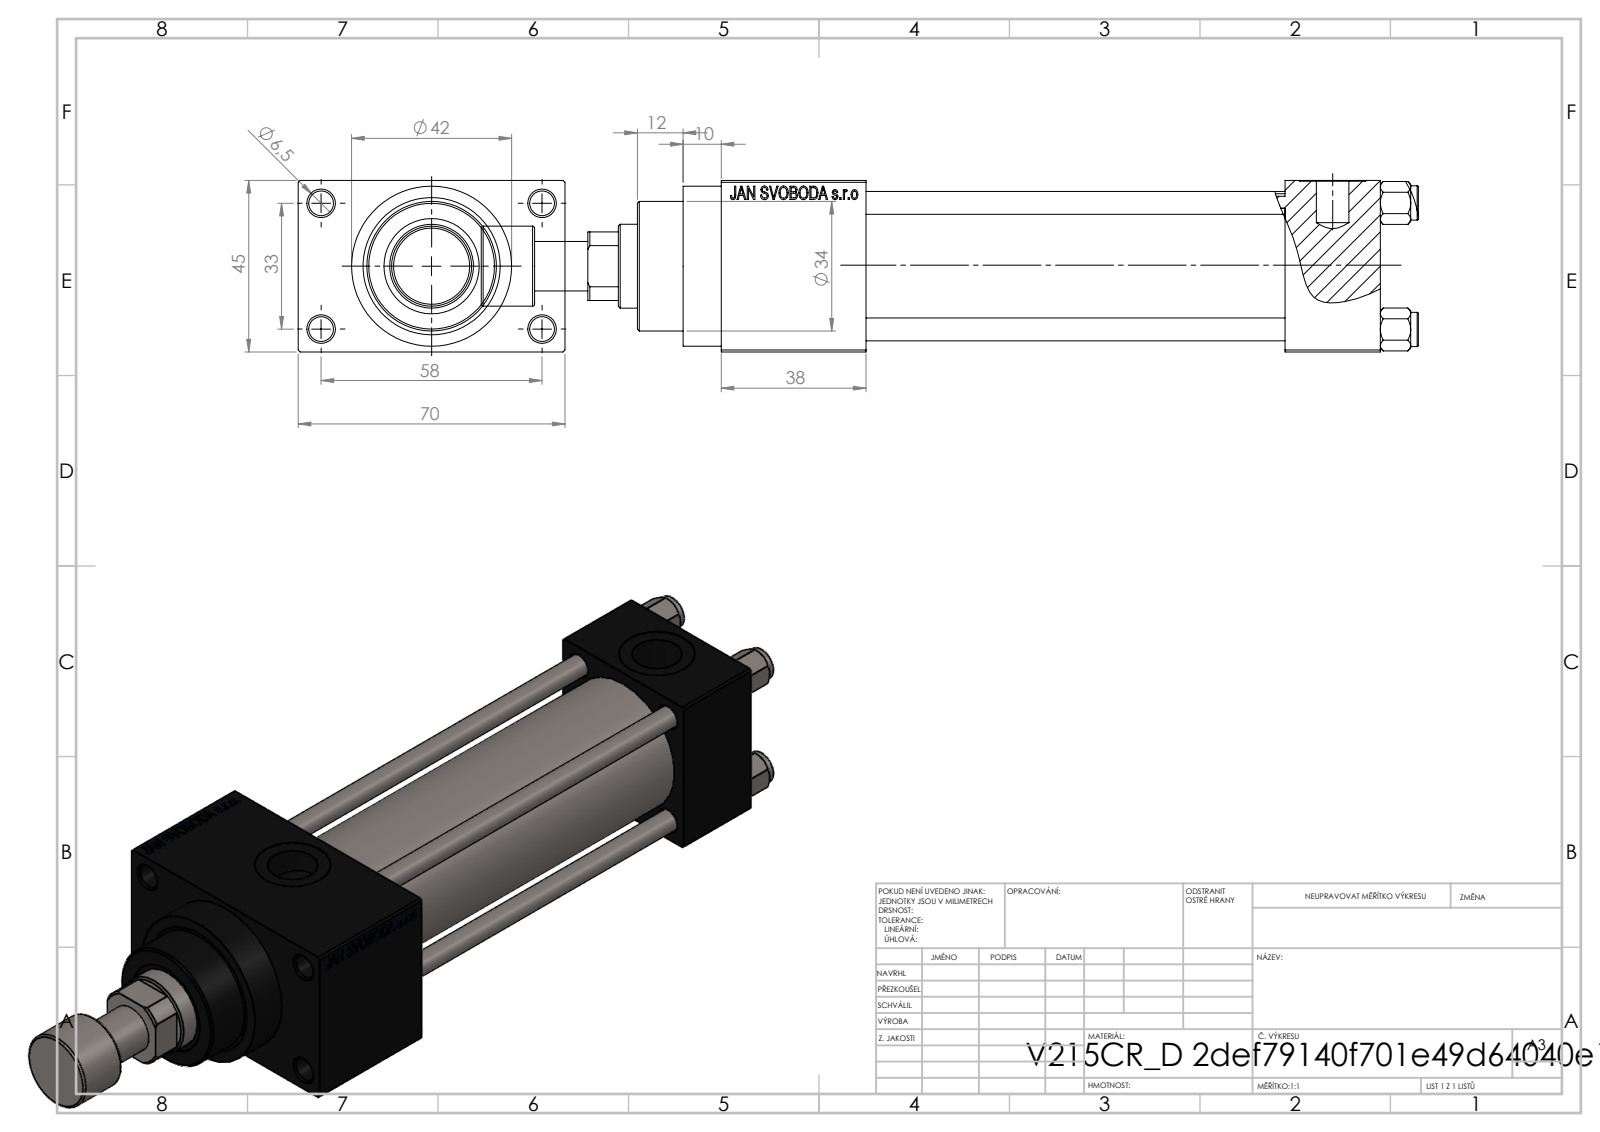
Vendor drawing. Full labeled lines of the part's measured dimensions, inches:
Part name (STEP PRODUCT): V215CR_D_TYCINKA; V215_VC_A; NUT_M5_D; V215CR_D_Body (+2 more)
STEP written by: SolidWorks 2019 (CONFIG_CONTROL_DESIGN)
Units: inches
Bodies: 12 solids, 1116 faces (499 planar, 93 cylindrical, 524 other)
Overall size (bounding box): 9.685 × 2.756 × 1.772
Volume: 18.34 in³ · Surface area: 160.3 in²
Round holes (diameter × count): ⌀0.236 ×4, ⌀0.256 ×4, ⌀0.276 ×2, ⌀0.518 ×2, ⌀0.787 ×2, ⌀0.413 ×1, ⌀0.866 ×1, ⌀0.945 ×1, ⌀0.984 ×1, ⌀1.26 ×1, ⌀1.299 ×1
Round bosses / shafts (diameter × count): ⌀0.354 ×4, ⌀1.654 ×1, ⌀1.496 ×1, ⌀1.339 ×1, ⌀0.827 ×1, ⌀0.512 ×1
Main face-to-face distances: 1.772, 0.984, 0.492, 2.264, 4.331, 5.315, 5.827, 2.756, 1.496, 6.811
Hole centre spacings: 0.488, 0.924, 1.307, 1.314, 1.392, 1.795, 2.219, 1.299
